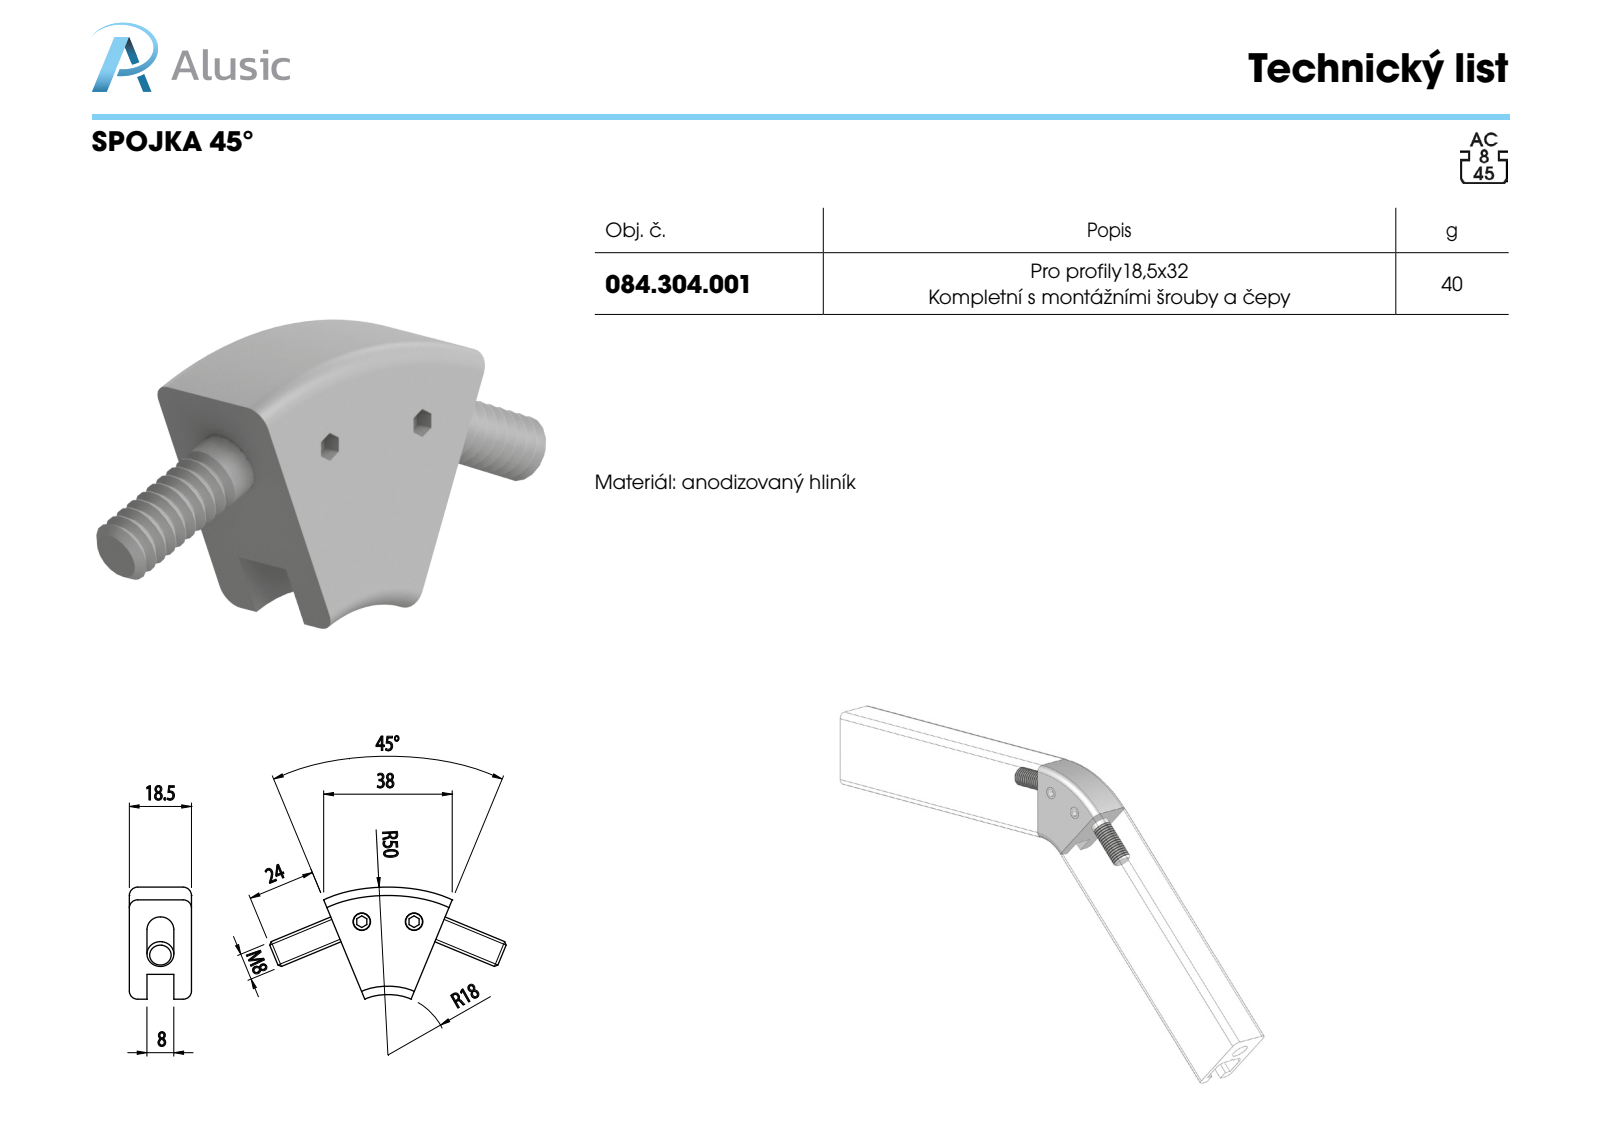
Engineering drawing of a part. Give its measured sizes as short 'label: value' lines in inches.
name: 084.304.001; 203208; 101832X45; GRANI A PUNTA PIATTA UNI 5923_M6x8 UNI 5923
written by: SolidWorks 2011 (CONFIG_CONTROL_DESIGN)
unit: in
bodies: 5 solids, 96 faces (28 planar, 26 cylindrical, 42 other)
size: 2.757 × 1.314 × 0.728
volume: 0.994 in³; area: 10.84 in²
holes: 2× ⌀0.197, 2× ⌀0.315
bosses: 2× ⌀0.315, 2× ⌀0.236
rounds: 1× R0.709, 1× R1.024, 1× R1.969
face distances: 0.728, 0.207, 0.522, 0.315, 0.473, 0.413, 0.108, 0.787, 1.26, 0.787
hole spacings: 0.613
